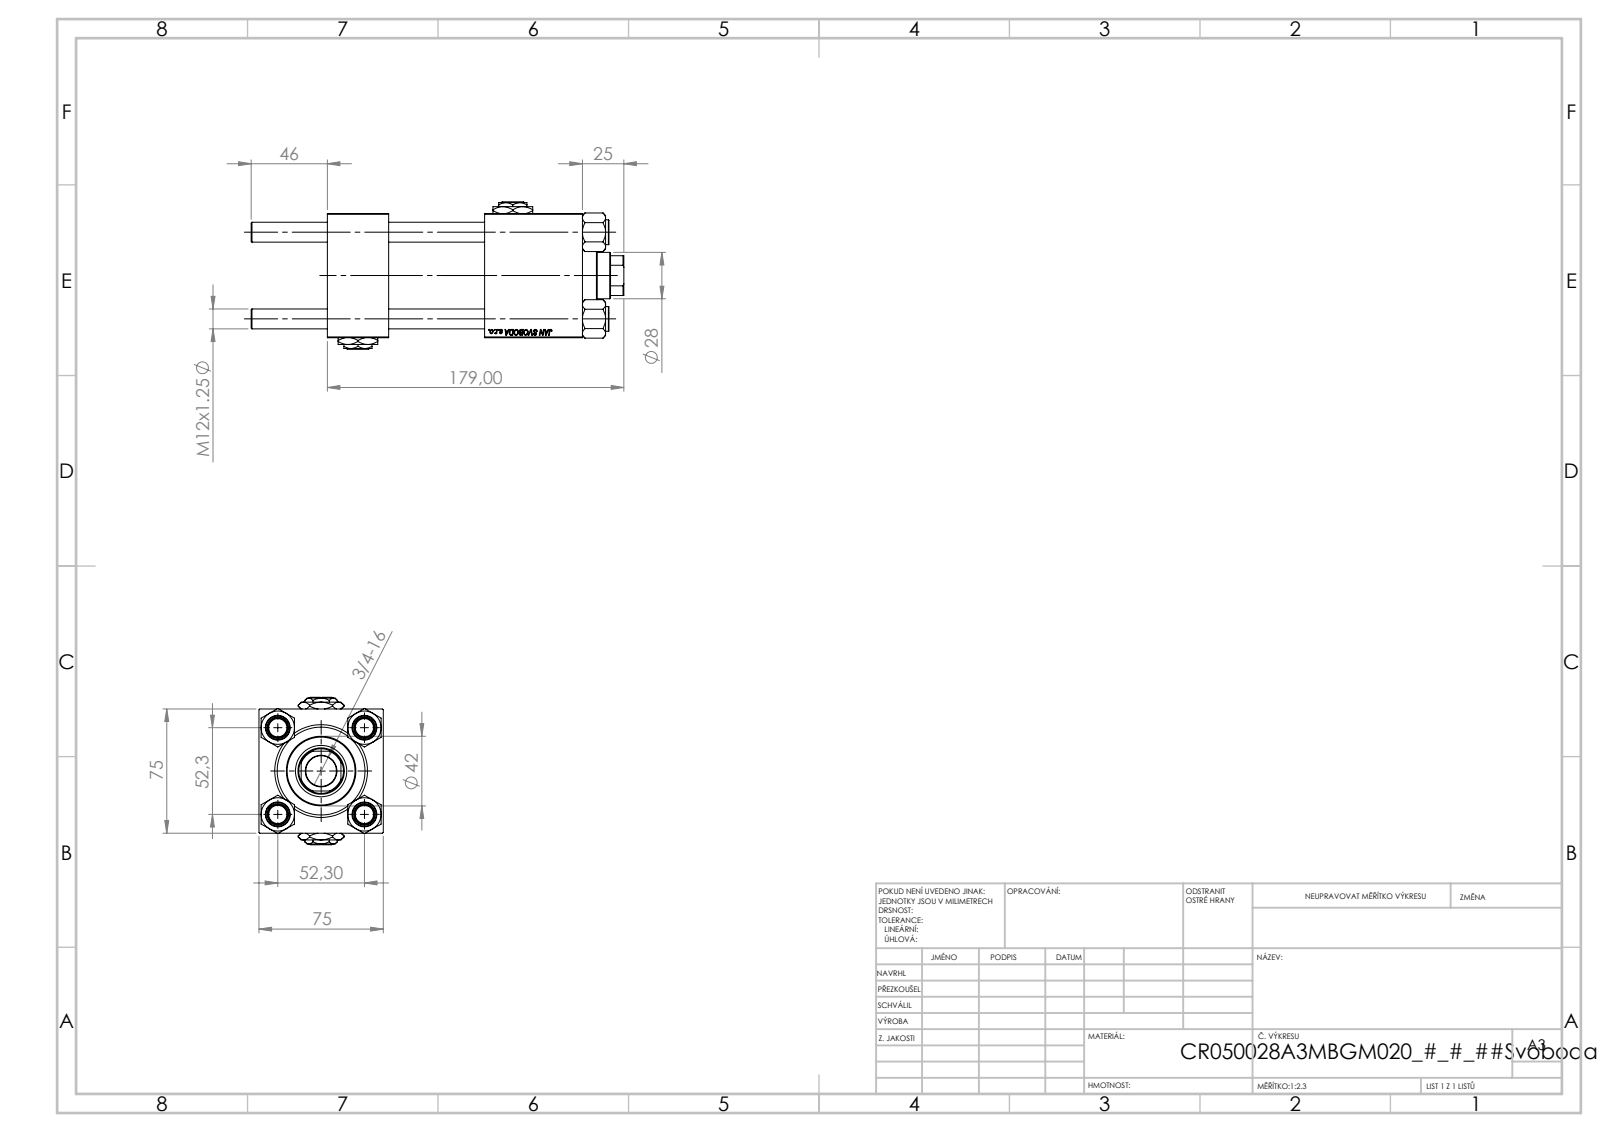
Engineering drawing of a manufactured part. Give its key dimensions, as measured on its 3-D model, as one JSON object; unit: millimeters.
{"part_name": "V215_VC_A; V215CR_BODY_A; V215CR_VCP; Zatka_pro_OIL_PORT (+2 more)", "step_written_by": "SolidWorks 2019 (CONFIG_CONTROL_DESIGN)", "units": "millimeters", "bodies": {"solids": 13, "faces": 1233, "planar": 567, "cylindrical": 88, "other": 578}, "overall_size": [225, 89, 75], "volume_mm3": 697084, "surface_area_mm2": 171866, "round_holes": [[12, 4], [7, 2], [20.96, 2], [30, 2], [18.5, 1], [28, 1], [31, 1], [41, 1], [50, 1], [53, 1]], "round_bosses_or_shafts": [[15, 4], [56, 1], [42, 1]], "partial_cylinders_radius": [[13.5, 1]], "face_to_face_distances": [75, 37, 154, 117, 95, 59, 58, 125.3, 88.3, 30.3], "hole_center_spacings": [36.98, 52.3, 73.96, 93.5]}
